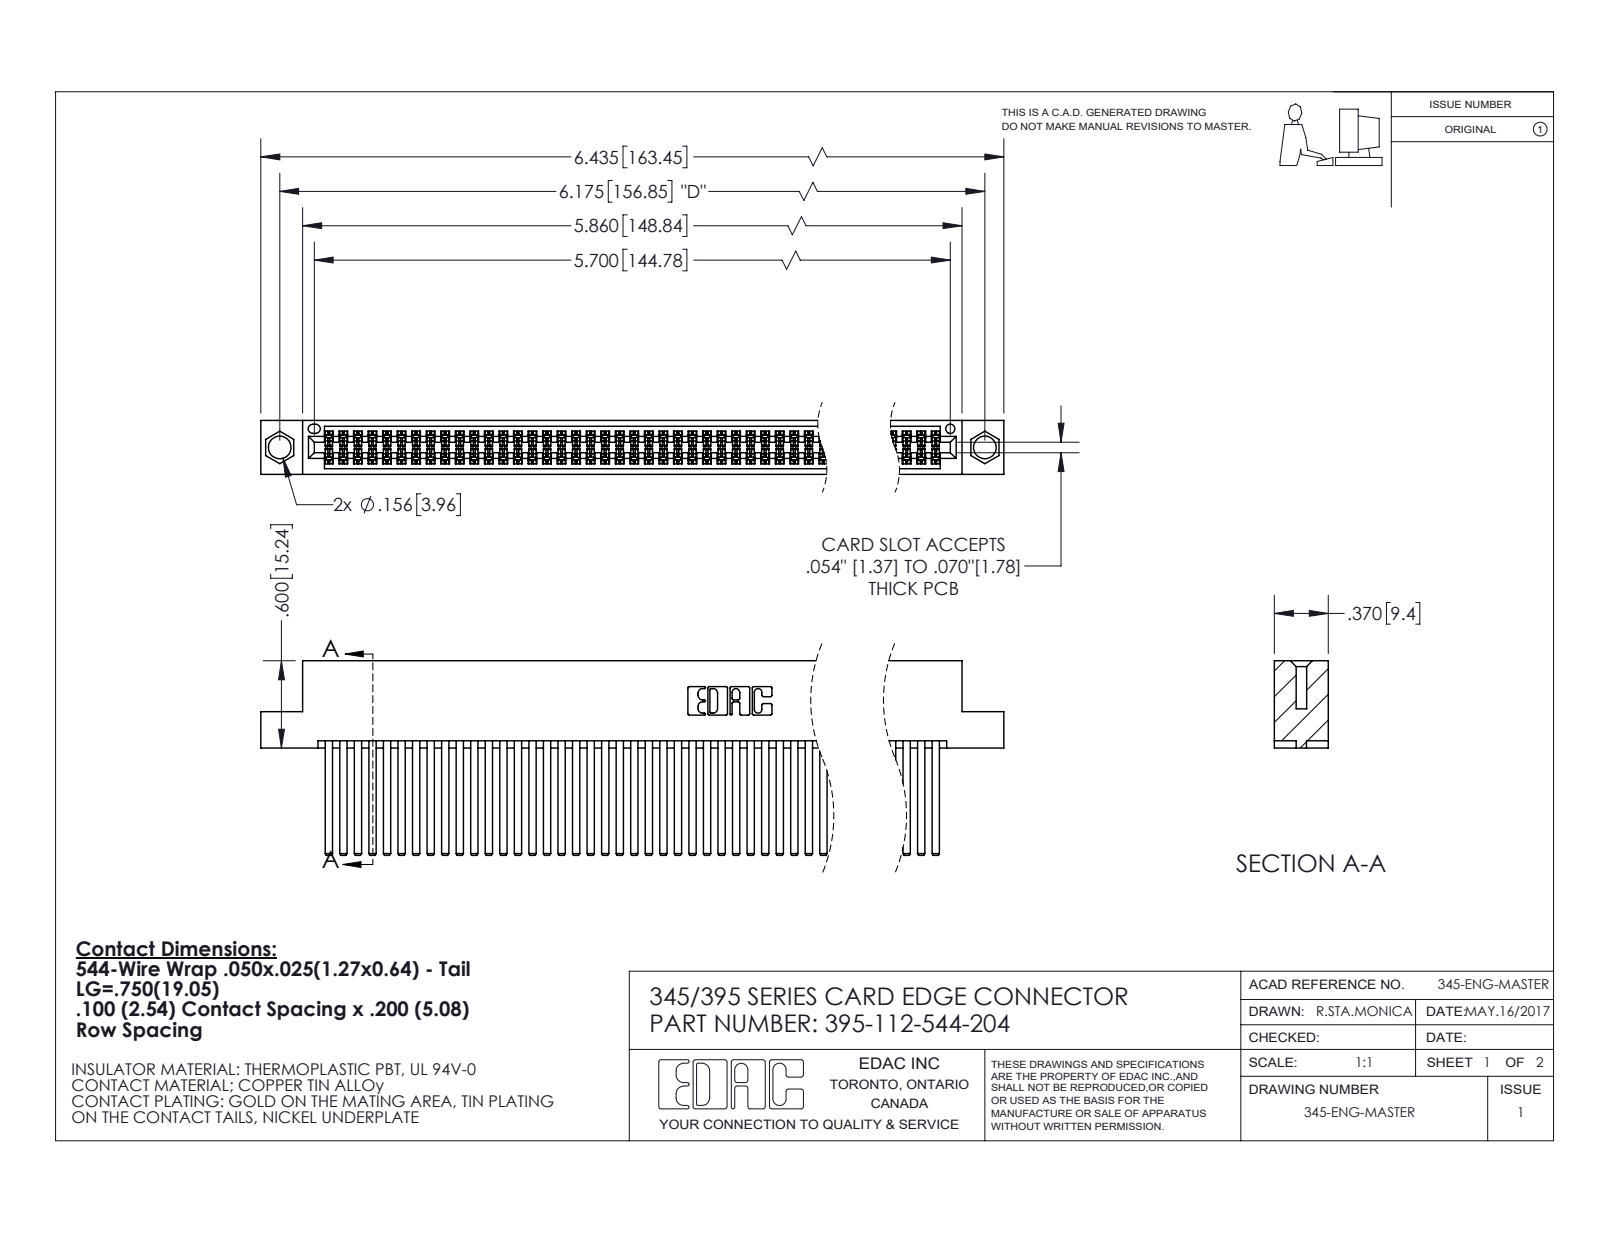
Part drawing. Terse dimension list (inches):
name: 395-112-544-204; 345-292-001_345-293-144; 345 Part_Flush Mounting Lugs - 0.156 Dia-TI
written by: SolidWorks 2020 (CONFIG_CONTROL_DESIGN)
unit: in
bodies: 113 solids, 5068 faces (3342 planar, 1726 cylindrical, 0 other)
size: 6.435 × 1.337 × 0.37
volume: 1.066 in³; area: 47.35 in²
holes: 2× ⌀0.156, 1× ⌀0.064
rounds: 169× R0.006, 22× R0.01, 6× R0.007, 6× R0.031, 3× R0.026, 2× R0.014, 2× R0.019, 2× R0.022
face distances: 0.2, 0.025, 0.298, 0.072, 0.098, 0.272, 0.225, 0.175, 0.37, 0.05
hole spacings: 0.27, 5.939, 6.175
